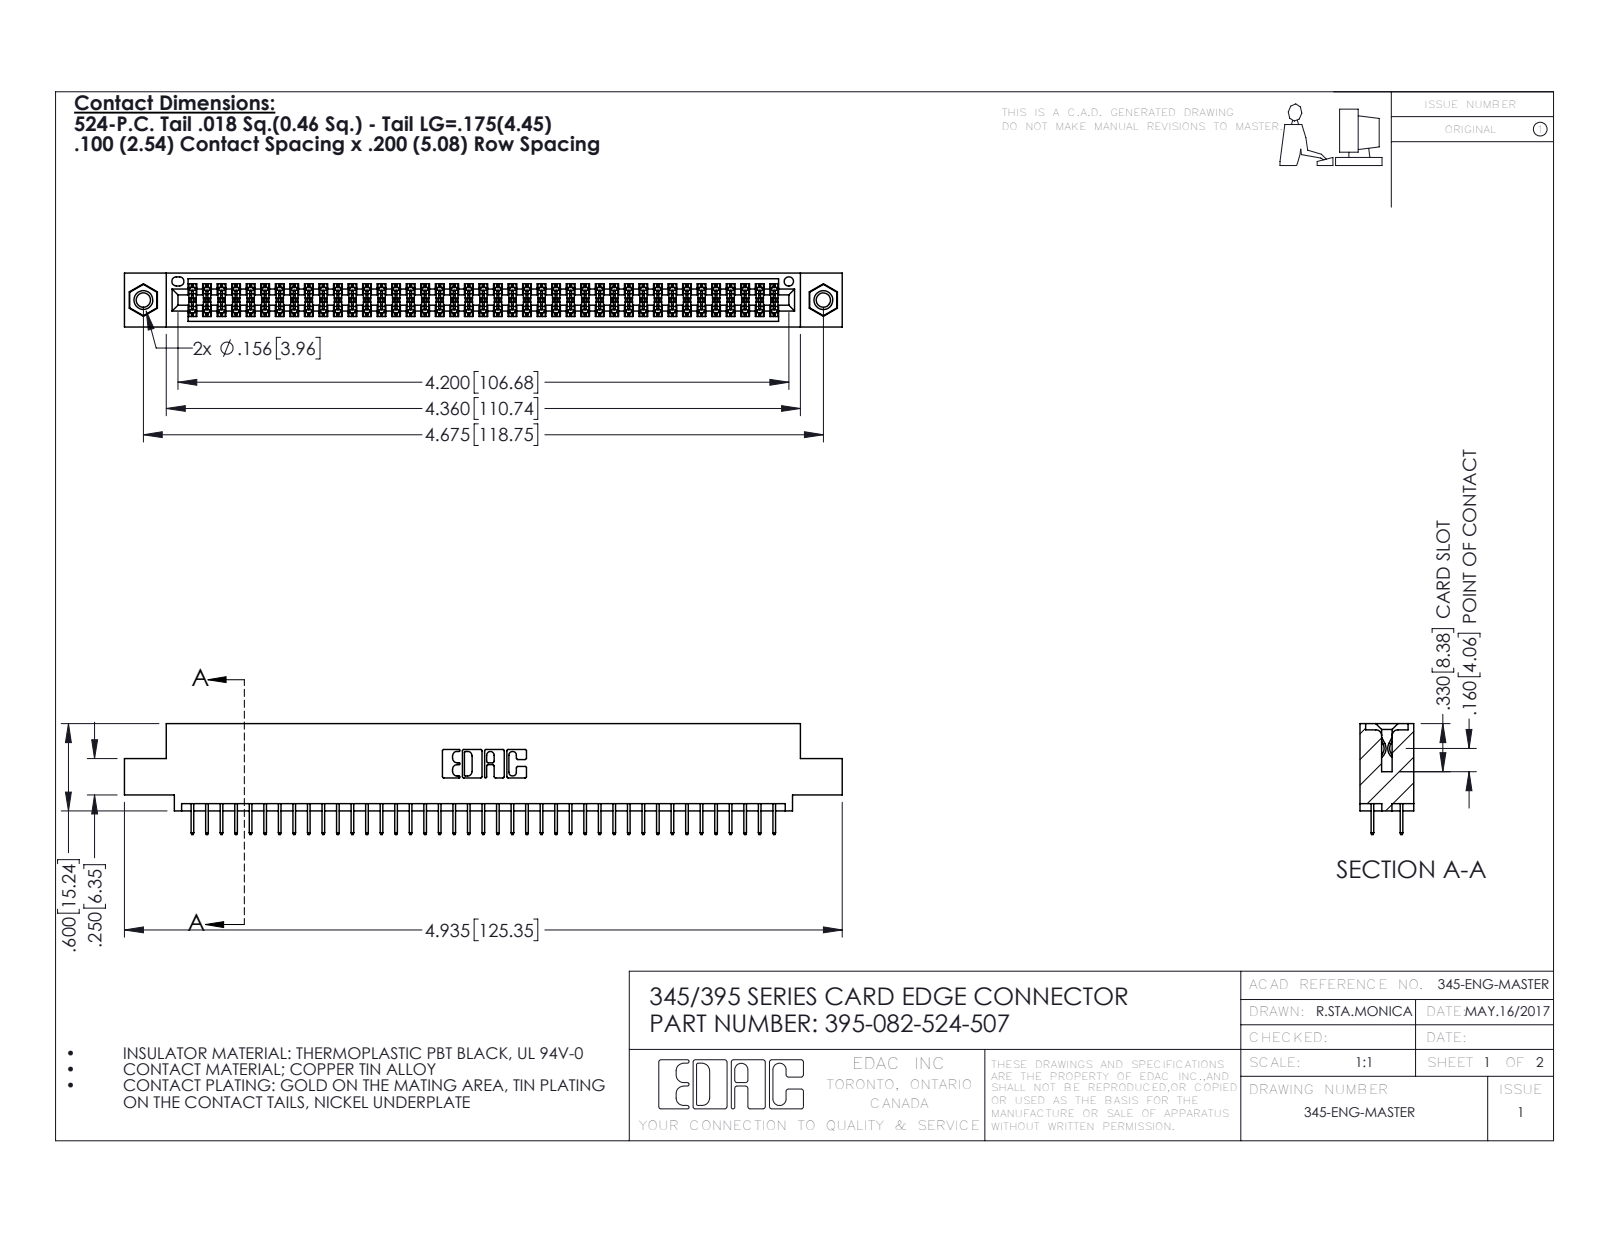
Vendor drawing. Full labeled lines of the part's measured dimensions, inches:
Part name (STEP PRODUCT): 395-082-524-507; 345 Part_0.110 Offset - 0.156 Dia-TI; 345-292-001_345-293-124; 345-250-001_345-250-005-103
STEP written by: SolidWorks 2016 (CONFIG_CONTROL_DESIGN)
Units: inches
Bodies: 85 solids, 4618 faces (3314 planar, 1288 cylindrical, 16 other)
Overall size (bounding box): 4.935 × 0.762 × 0.37
Volume: 0.73 in³ · Surface area: 27.04 in²
Round holes (diameter × count): ⌀0.098 ×2, ⌀0.125 ×2, ⌀0.156 ×2, ⌀0.064 ×1
Round bosses / shafts (diameter × count): ⌀0.155 ×2
Partial cylindrical surfaces — rounded edges, fillets, slot ends (radius × count): R0.006 ×123, R0.01 ×22, R0.007 ×6, R0.031 ×6, R0.026 ×3, R0.014 ×2, R0.019 ×2, R0.022 ×2
Main face-to-face distances: 0.072, 0.298, 0.2, 0.37, 0.098, 0.272, 0.025, 0.225, 0.072, 0.175
Hole centre spacings: 0.27, 4.439, 4.675
